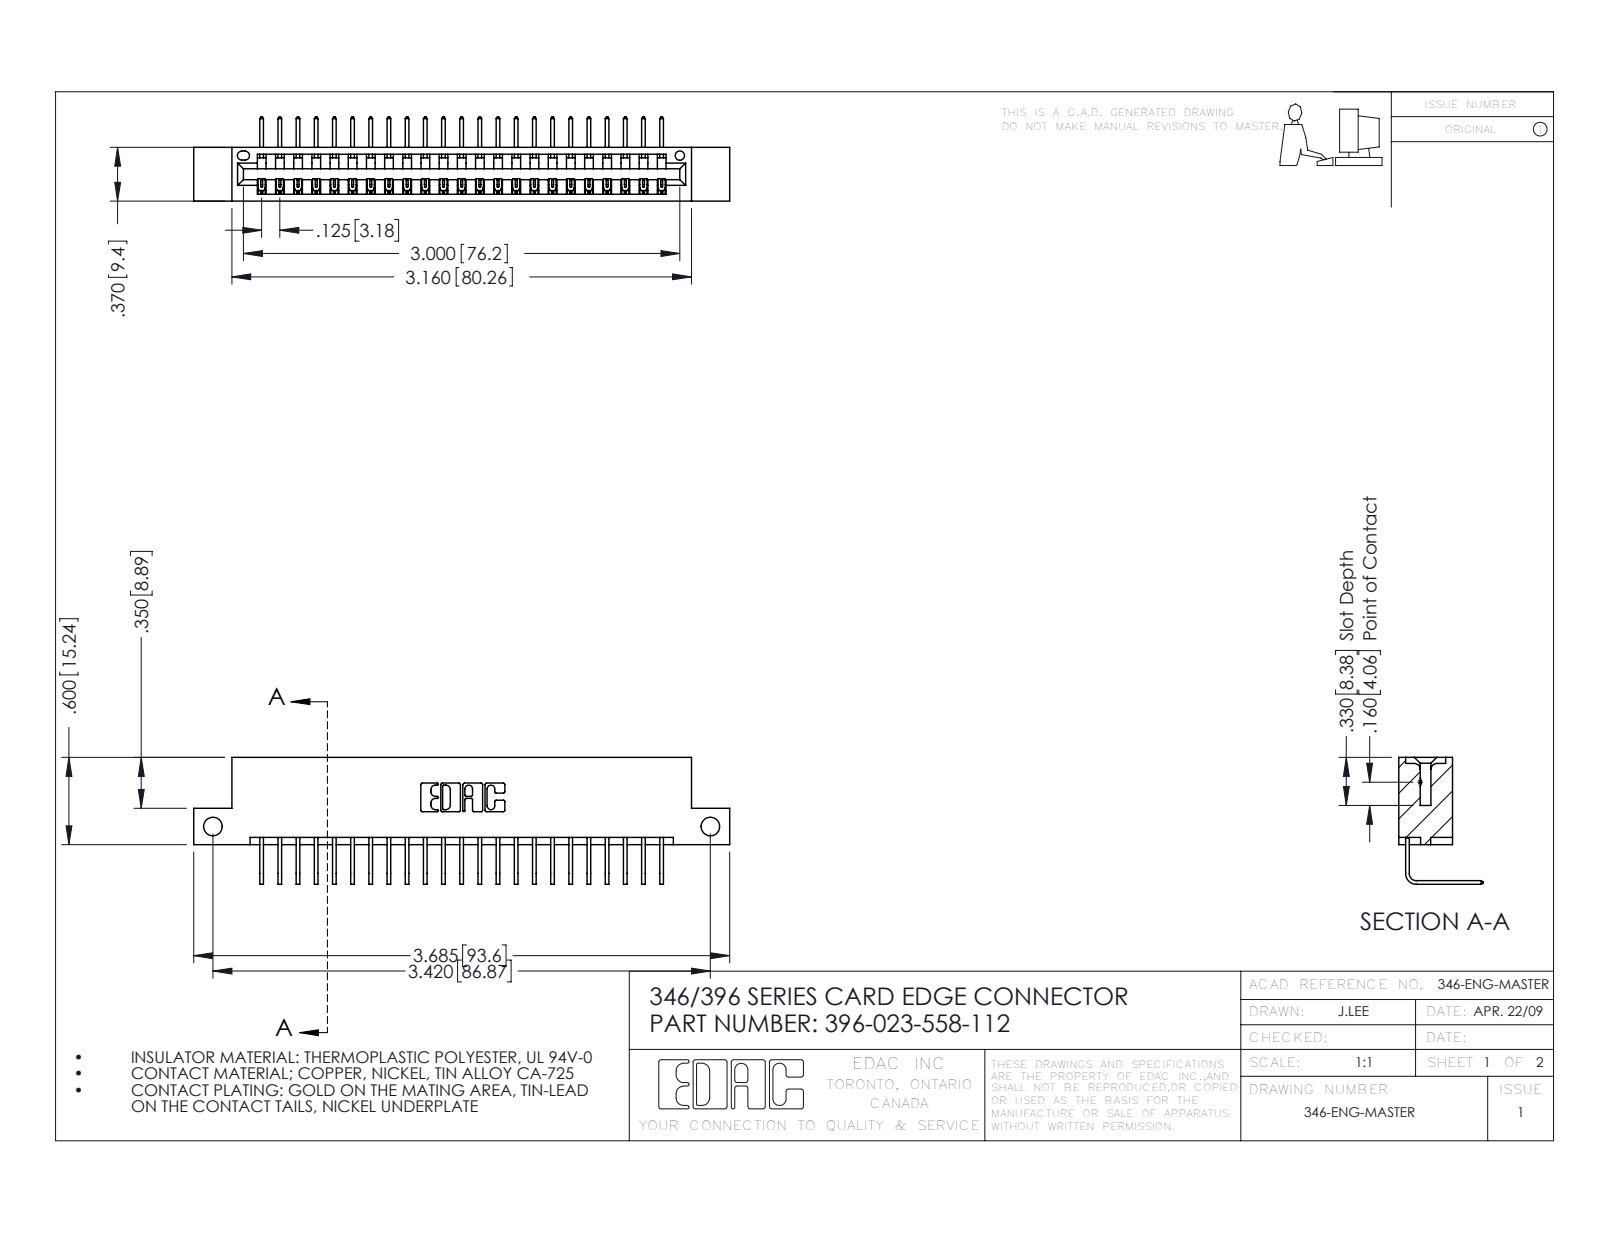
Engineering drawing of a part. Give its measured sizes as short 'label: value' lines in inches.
name: 345-292-001_558 Tail - 2; 396-023-558-112; 346 Part_Flush Mounting Lugs - Side Mount
written by: SolidWorks 2016 (CONFIG_CONTROL_DESIGN)
unit: in
bodies: 24 solids, 1502 faces (1042 planar, 460 cylindrical, 0 other)
size: 3.685 × 0.873 × 0.58
volume: 0.538 in³; area: 17.25 in²
holes: 2× ⌀0.128, 1× ⌀0.064
rounds: 46× R0.006, 22× R0.01, 6× R0.007, 6× R0.031, 3× R0.026, 2× R0.031, 2× R0.04, 1× R0.014
face distances: 0.322, 0.048, 0.25, 0.37, 0.298, 0.025, 0.072, 0.148, 0.222, 0.1
hole spacings: 3.42
